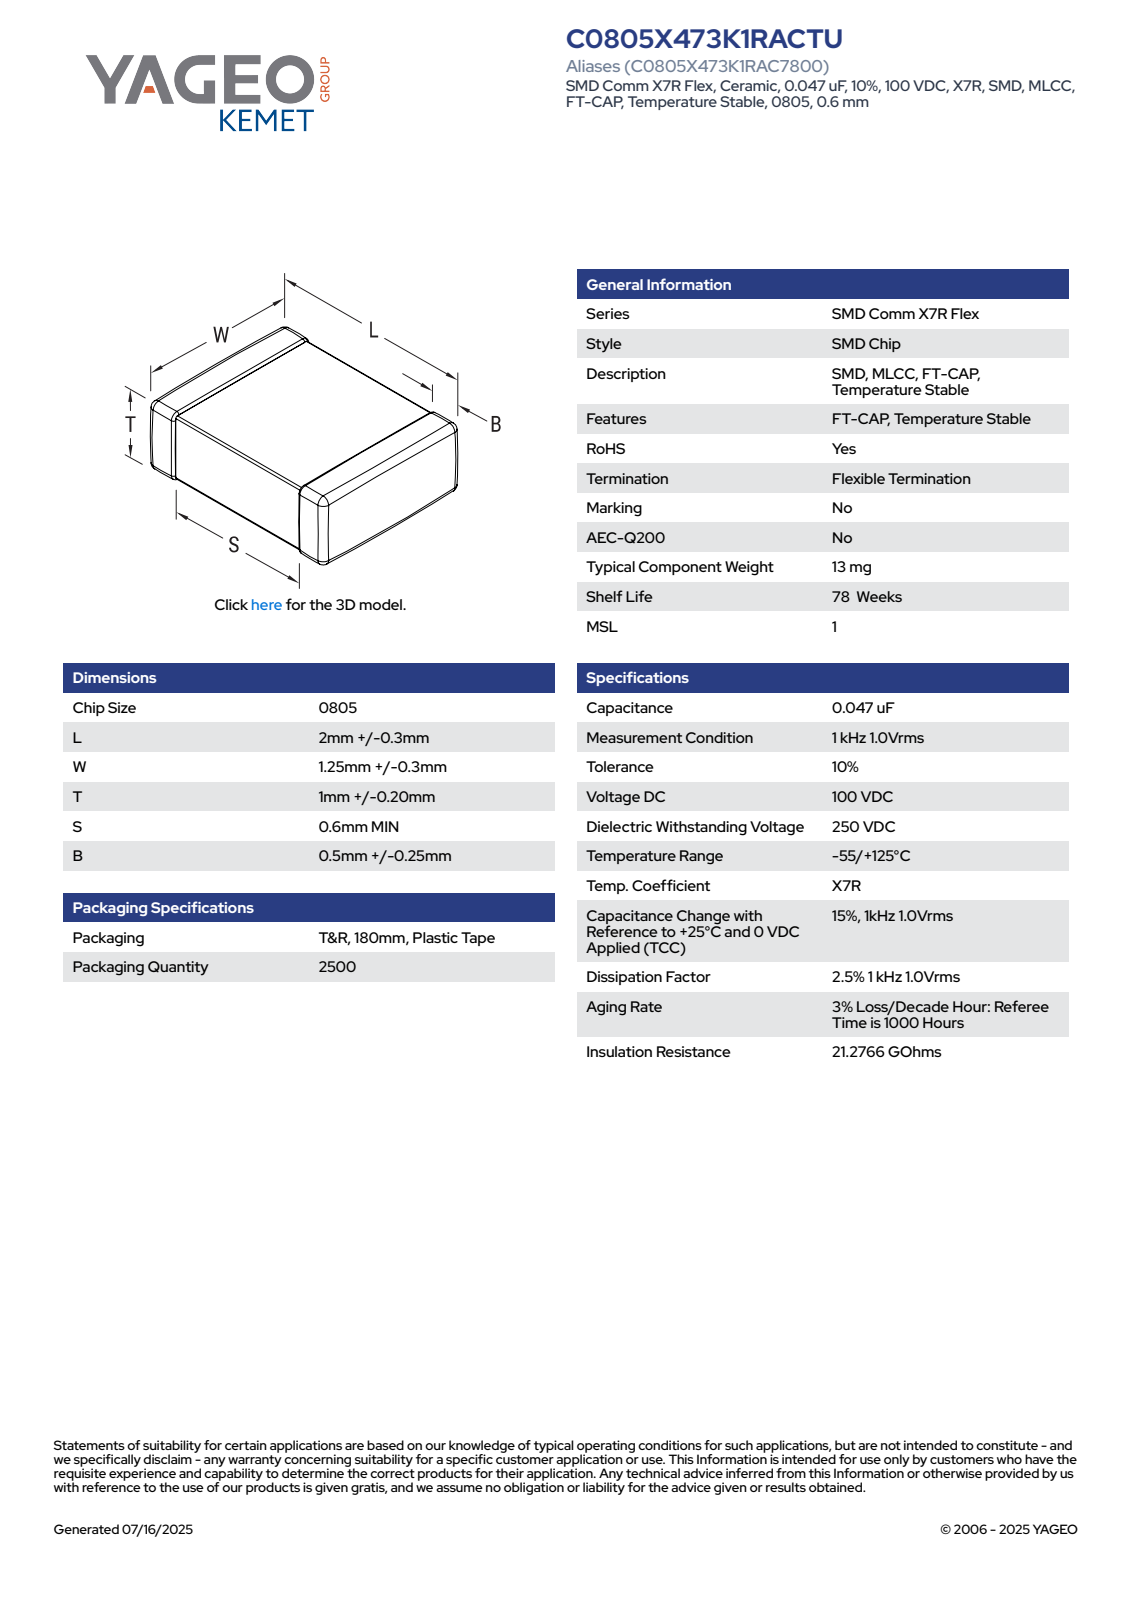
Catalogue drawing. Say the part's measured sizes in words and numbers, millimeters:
The part is named "CCS_CCSTD_0805_L2.3W1.55T1.2B0.5". Its 3-D file was written by "SolidWorks 2014 (AUTOMOTIVE_DESIGN)". It is 4 solids with 125 faces: 71 planar, 38 cylindrical and 16 other. Overall it measures 2.3 by 1.55 by 1.2 millimeters. Its volume is 4 cubic millimeters and its surface area 16 square millimeters. The main face-to-face distances are 1.17, 1.52, 1.14, 2.3, 1.49, 1.2, 1.55, 1.06, 1.24, 1.01.
